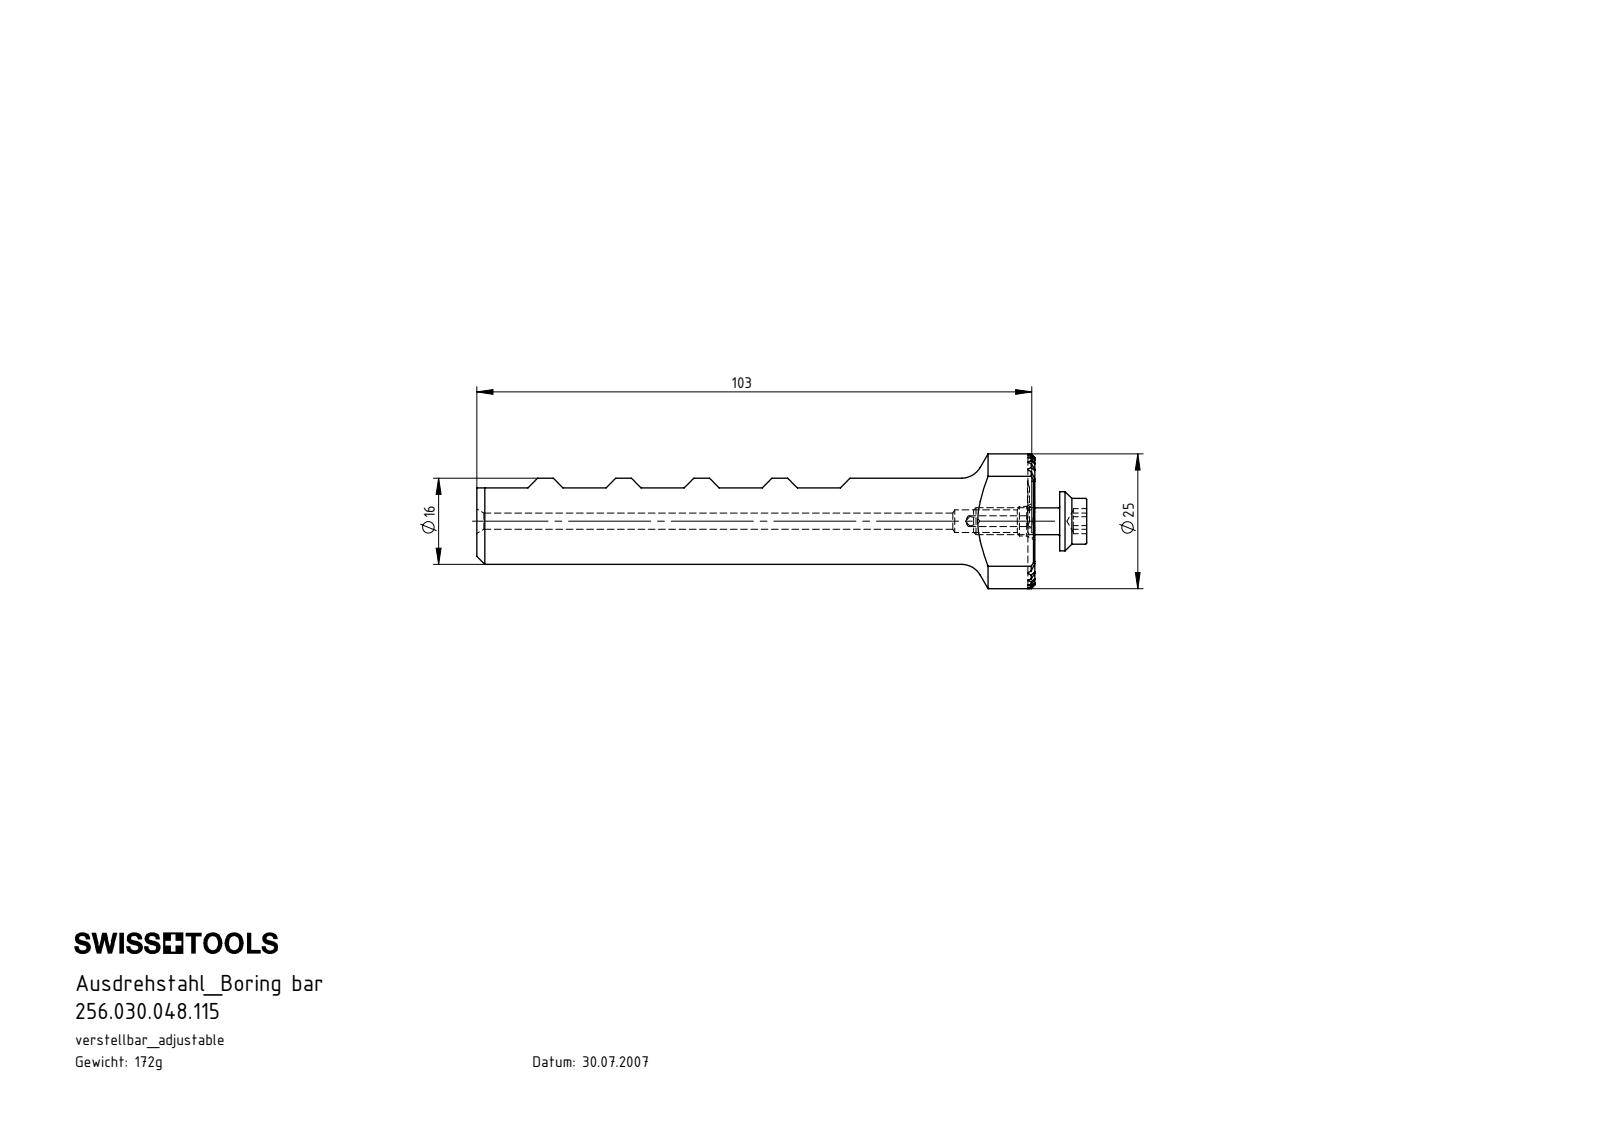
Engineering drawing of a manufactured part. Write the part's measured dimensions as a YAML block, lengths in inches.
part_name: "BN 1392 - M5 x 16; U16-BV1.K01.103_A; U16.BV1.K01.103"
step_written_by: "SolidWorks 2017 (AUTOMOTIVE_DESIGN)"
units: inches
bodies: {solids: 2, faces: 138, planar: 78, cylindrical: 26, other: 34}
overall_size: [4.457, 0.984, 0.732]
volume: 1.334
surface_area: 12.45
round_holes:
  - {diameter: 0.079, count: 1}
  - {diameter: 0.118, count: 1}
  - {diameter: 0.165, count: 1}
  - {diameter: 0.217, count: 1}
round_bosses_or_shafts:
  - {diameter: 0.63, count: 1}
  - {diameter: 0.433, count: 1}
  - {diameter: 0.335, count: 1}
  - {diameter: 0.197, count: 1}
partial_cylinders:
  - {radius: 0.006, count: 9}
  - {radius: 0.049, count: 2}
  - {radius: 0.492, count: 1}
face_to_face_distances: [0.068, 0.341, 0.273, 0.136, 0.205, 0.732, 0.137, 0.204, 0.404, 0.409]
